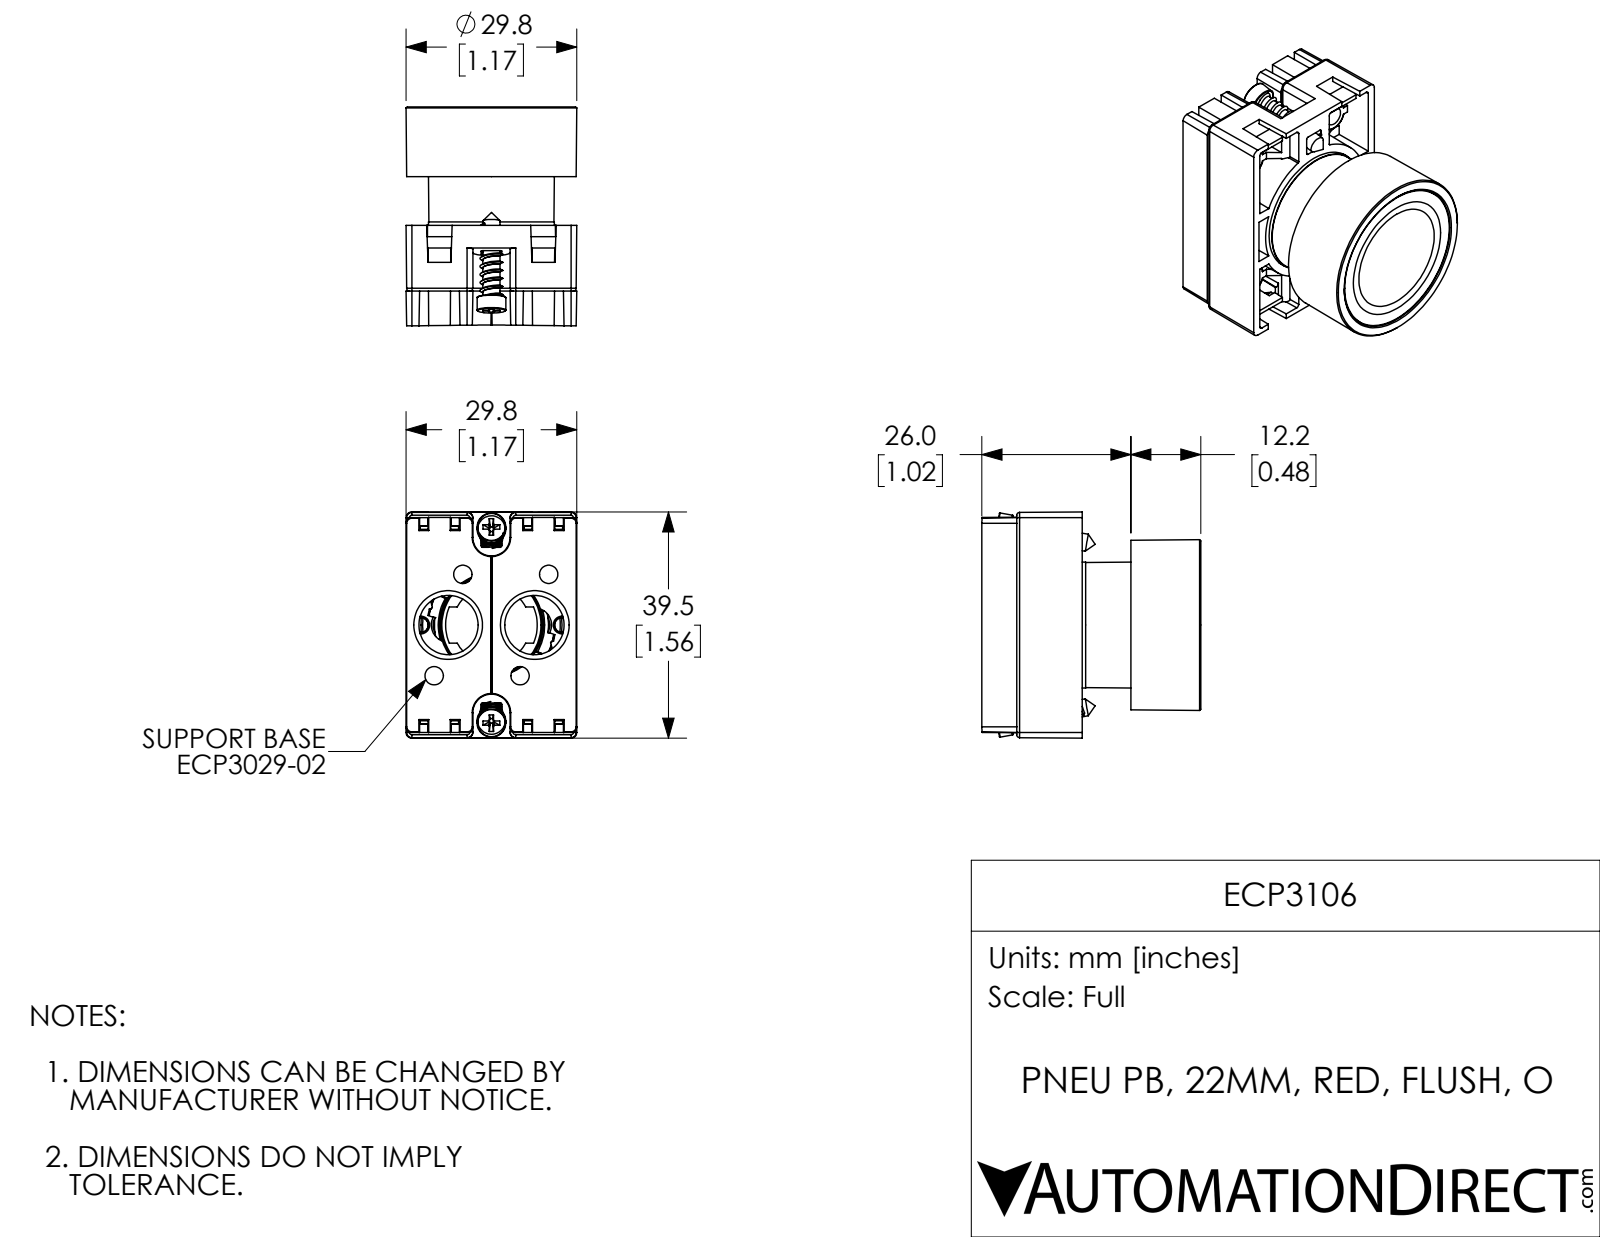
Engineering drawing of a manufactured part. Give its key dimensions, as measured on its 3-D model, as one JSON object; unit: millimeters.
{"part_name": "ECP3106", "step_written_by": "SolidWorks 2017 (AUTOMOTIVE_DESIGN)", "units": "millimeters", "bodies": {"solids": 7, "faces": 778, "planar": 363, "cylindrical": 131, "other": 284}, "overall_size": [39.5, 38.2, 29.8], "volume_mm3": 14600, "surface_area_mm2": 18730, "round_holes": [[2.1, 4], [10.3, 2], [17.7, 1], [18.6, 1]], "round_bosses_or_shafts": [[5, 2], [3, 2], [25.8, 1], [22, 1]], "partial_cylinders_radius": [[0.5, 18], [0.2, 8], [0.3, 8], [0.2, 4], [1, 4], [0.2, 2], [3, 2], [3.3, 2]], "face_to_face_distances": [30.4, 24.5, 4.5, 1.7, 18.2, 18.9, 11.5, 14.9, 13.2, 6.5], "hole_center_spacings": [7.7, 13.7, 20.8, 7.5, 12, 24.7, 27.5, 15]}
